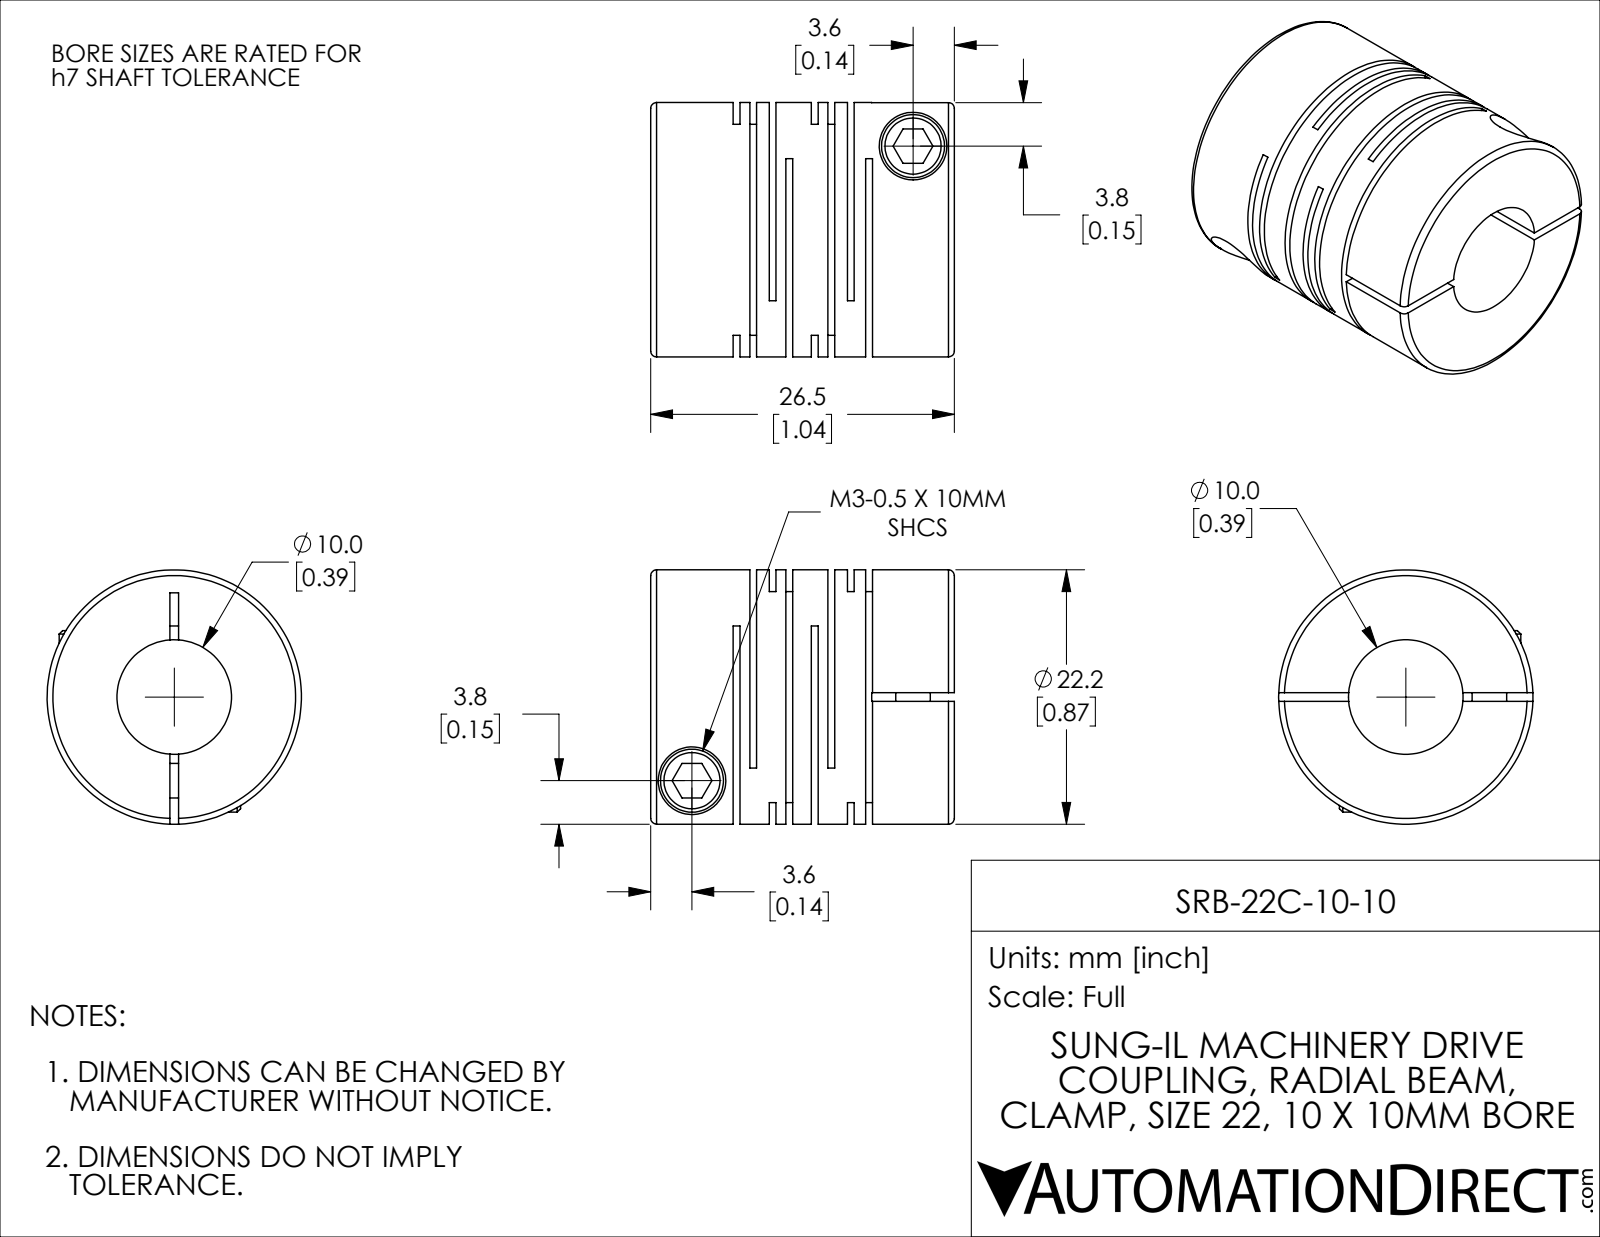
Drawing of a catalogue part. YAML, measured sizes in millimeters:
part_name: "SRB-22C-10-10"
step_written_by: "SolidWorks 2021 (CONFIG_CONTROL_DESIGN)"
units: millimeters
bodies: {solids: 1, faces: 115, planar: 60, cylindrical: 42, other: 13}
overall_size: [26.5, 22.2, 22.2]
volume: 6716
surface_area: 7436
round_holes:
  - {diameter: 3, count: 2}
  - {diameter: 5.9, count: 2}
  - {diameter: 10, count: 1}
round_bosses_or_shafts:
  - {diameter: 5.5, count: 2}
  - {diameter: 22.2, count: 1}
face_to_face_distances: [0.59, 3.15, 6.82, 1.45, 5.37, 3.67, 1.7, 2.56, 6.23, 0.86]
